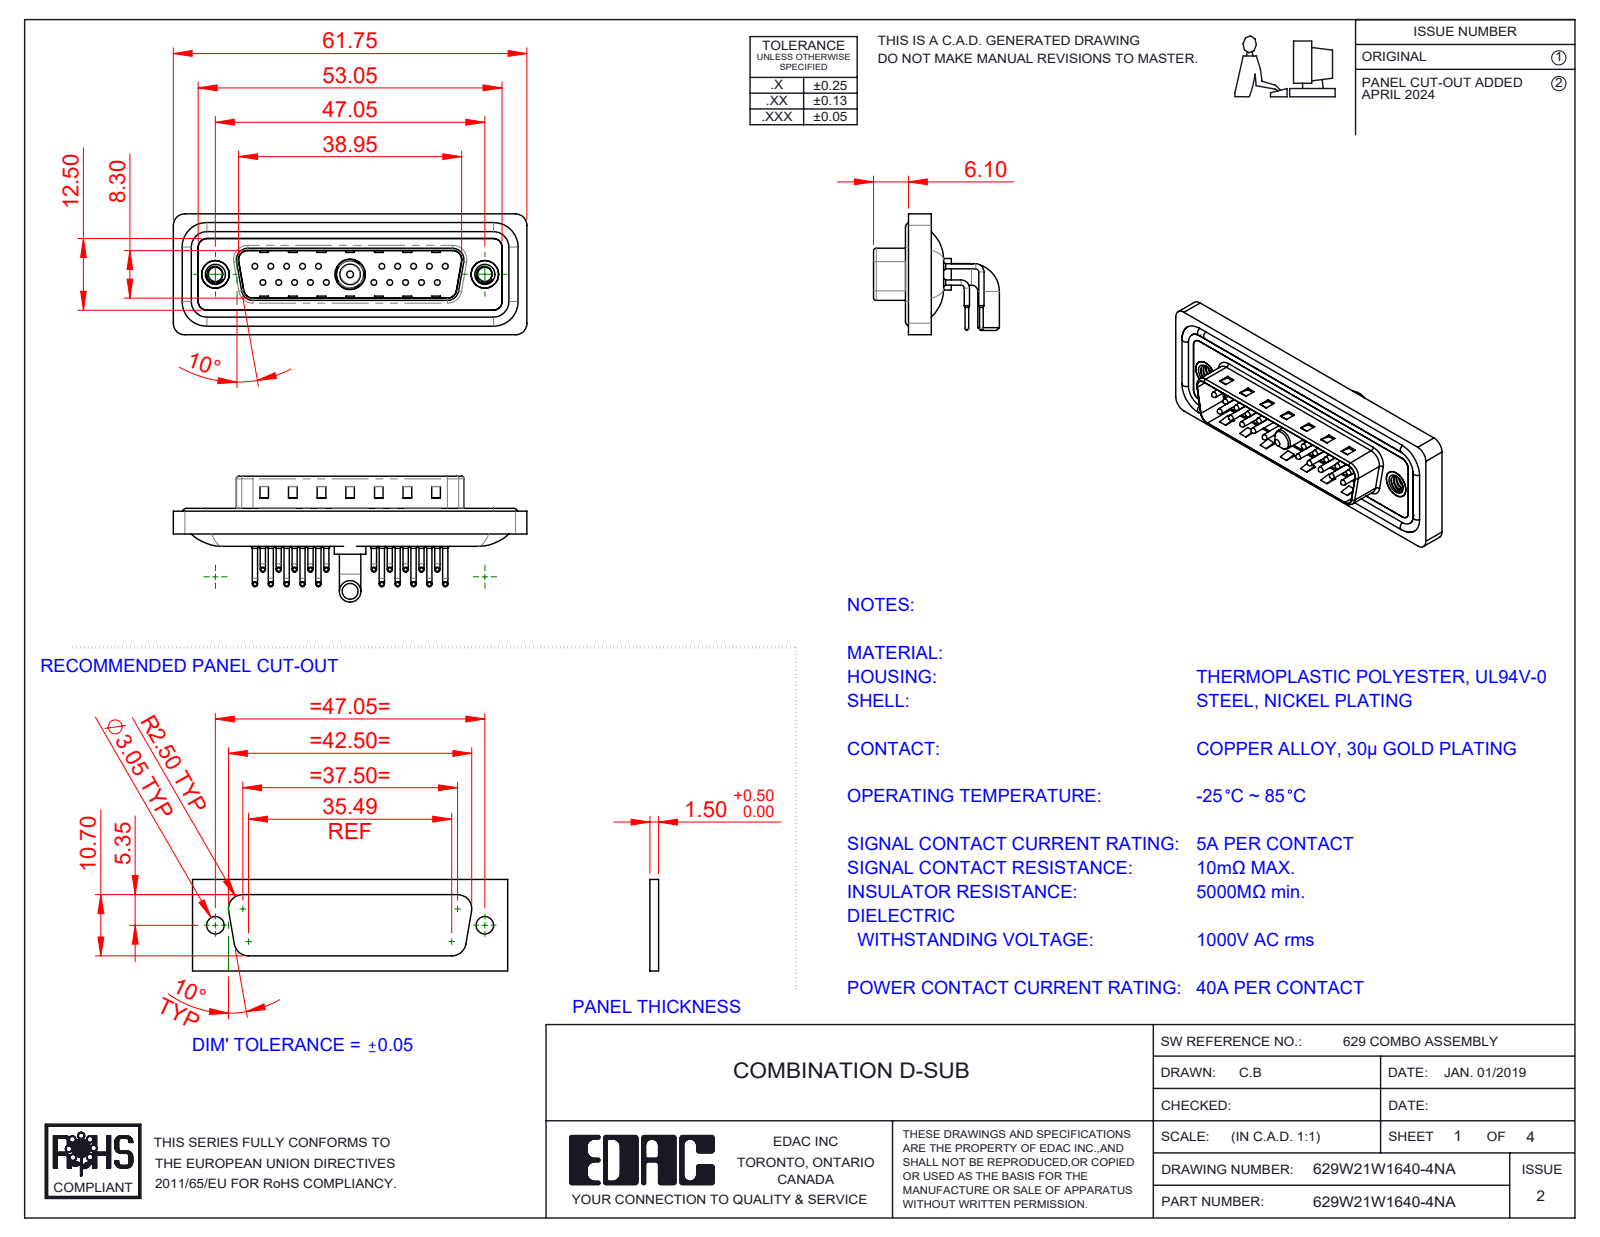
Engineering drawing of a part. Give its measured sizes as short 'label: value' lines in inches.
name: 629Combo Shell Front_25 Contacts; 629Combo Threaded Rivet_A; 629W21W1640-4NA; 629Combo Shell Rear_25 Contacts (+5 more)
written by: SolidWorks 2023 (CONFIG_CONTROL_DESIGN)
unit: in
bodies: 29 solids, 2720 faces (1499 planar, 927 cylindrical, 294 other)
size: 2.431 × 0.865 × 0.831
volume: 0.457 in³; area: 19.79 in²
holes: 20× ⌀0.03, 20× ⌀0.063, 20× ⌀0.079, 2× ⌀0.098, 2× ⌀0.157, 2× ⌀0.189, 2× ⌀0.197, 1× ⌀0.191, 1× ⌀0.209
bosses: 40× ⌀0.035, 20× ⌀0.059, 20× ⌀0.039, 20× ⌀0.026, 4× ⌀0.063, 2× ⌀0.193, 2× ⌀0.148, 1× ⌀0.217
rounds: 20× R0.04, 18× R0.059, 18× R0.079, 8× R0.02, 8× R0.063, 4× R0.01, 4× R0.024, 4× R0.026
face distances: 0.016, 0.114, 0.031, 0.161, 0.043, 0.083, 0.063, 0.177, 0.059, 0.098
hole spacings: 0.124, 0.109, 0.218, 0.327, 0.198, 0.763, 0.826, 0.872
